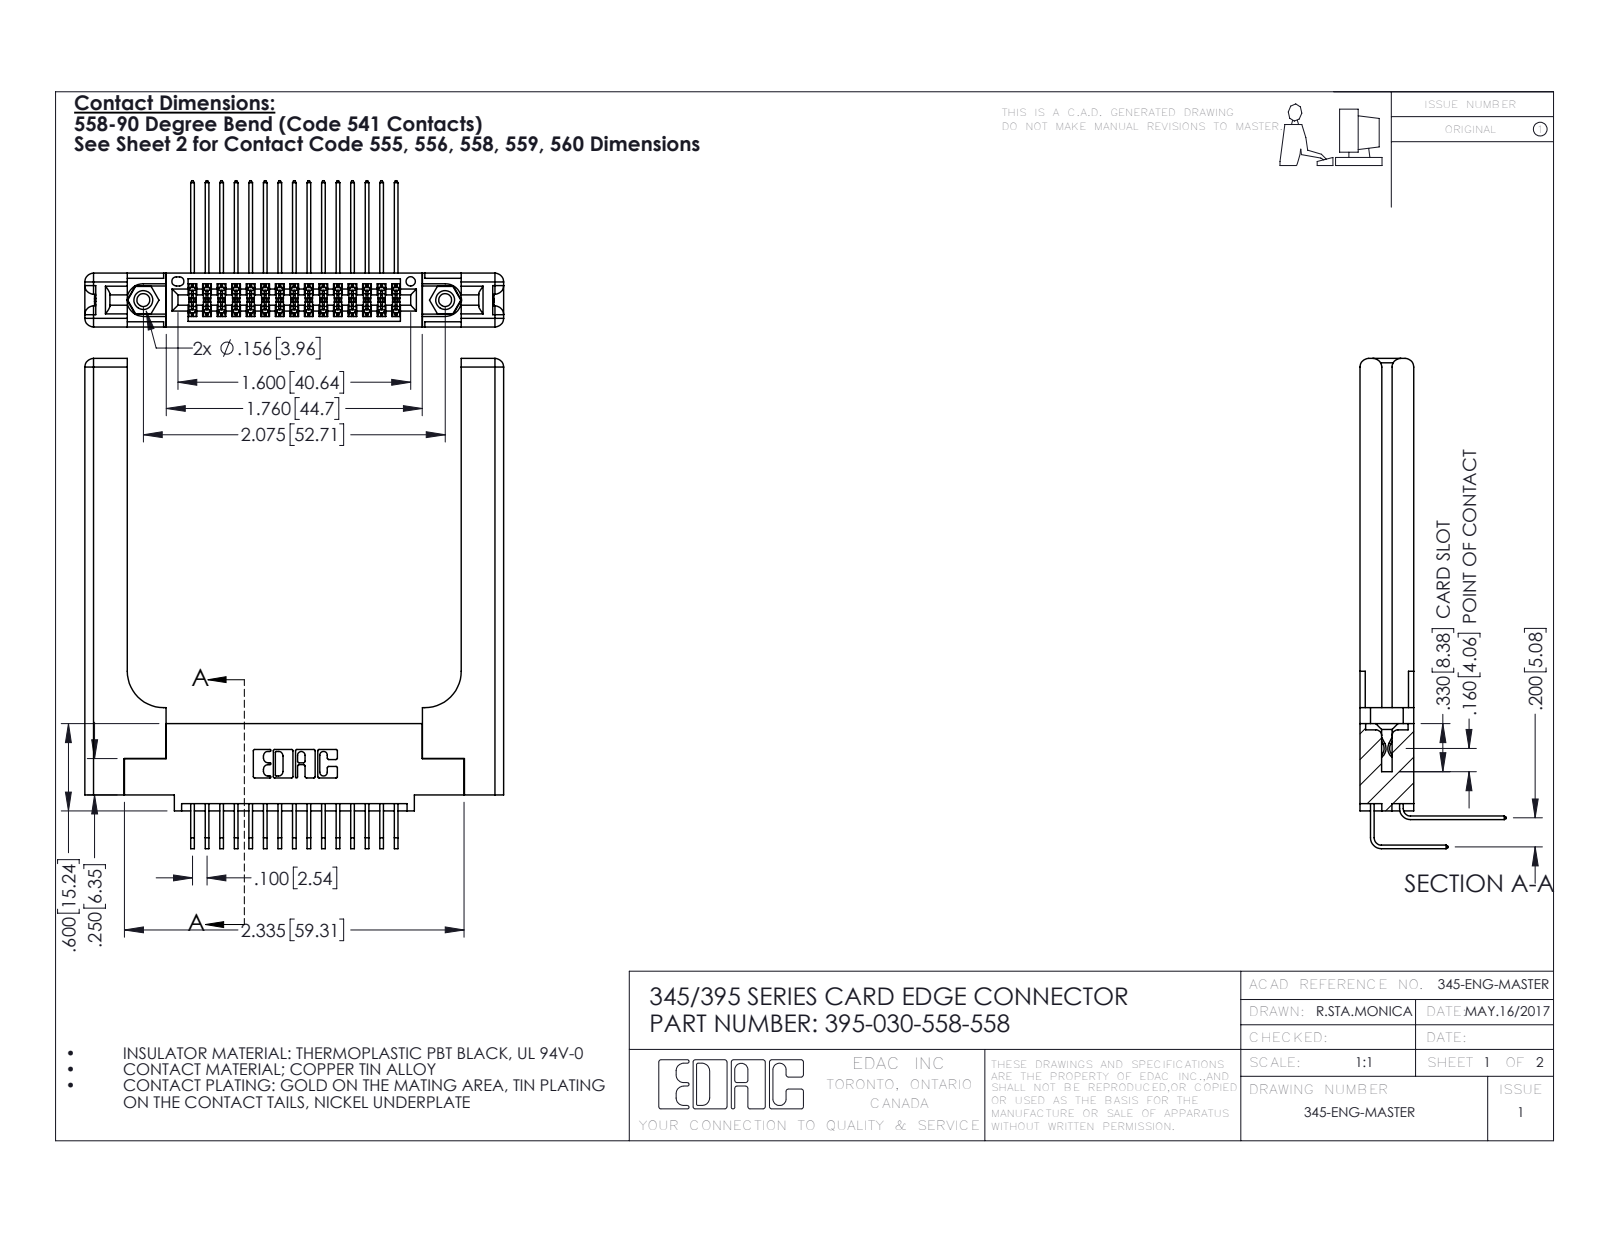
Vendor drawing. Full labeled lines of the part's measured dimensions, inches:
Part name (STEP PRODUCT): 345-292-001_558 Tail - 2; 345-292-001_558 559 Tail - 1; 345-220-058_345-220-058; 345-250-001_345-250-001-102 (+2 more)
STEP written by: SolidWorks 2016 (CONFIG_CONTROL_DESIGN)
Units: inches
Bodies: 35 solids, 1946 faces (1282 planar, 604 cylindrical, 60 other)
Overall size (bounding box): 3.369 × 2.879 × 1.005
Volume: 0.941 in³ · Surface area: 24.37 in²
Round holes (diameter × count): ⌀0.089 ×2, ⌀0.125 ×2, ⌀0.156 ×2, ⌀0.064 ×1
Round bosses / shafts (diameter × count): ⌀0.155 ×2
Partial cylindrical surfaces — rounded edges, fillets, slot ends (radius × count): R0.006 ×46, R0.01 ×22, R0.06 ×16, R0.007 ×6, R0.031 ×6, R0.026 ×3, R0.014 ×2, R0.019 ×2
Main face-to-face distances: 0.37, 0.072, 0.298, 0.148, 0.15, 0.077, 0.2, 0.22, 0.225, 0.098
Hole centre spacings: 0.27, 1.842, 2.075
